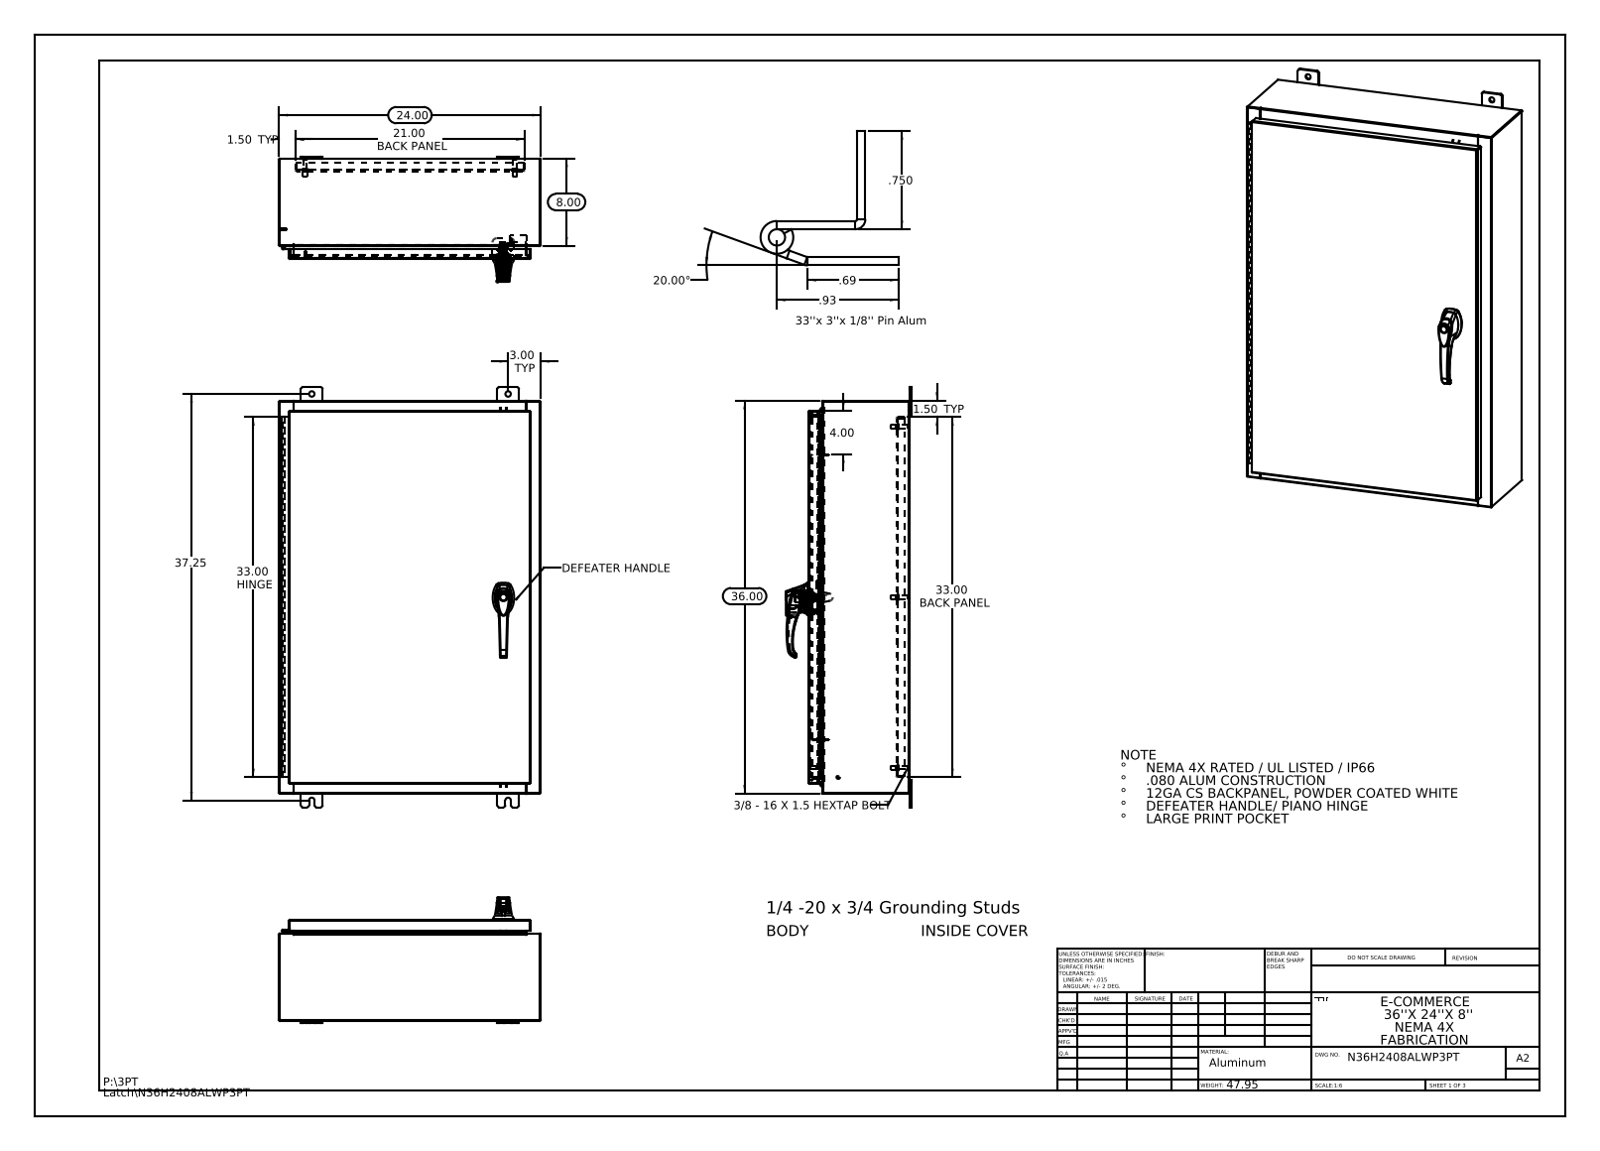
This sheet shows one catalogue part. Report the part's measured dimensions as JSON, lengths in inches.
{"part_name": "10_30 CD Stud; N36H2408ALWP3PT Backpanel; N36H2408ALWP3PT Hinge Cover Side; 297026 (+8 more)", "step_written_by": "SolidWorks 2013 (CONFIG_CONTROL_DESIGN)", "units": "inches", "bodies": {"solids": 39, "faces": 2856, "planar": 1053, "cylindrical": 1085, "other": 718}, "overall_size": [38.5, 24, 11.495], "volume_in3": 318.5, "surface_area_in2": 7860, "round_holes": [[0.5, 10], [0.25, 4], [0.138, 3], [0.161, 3], [0.079, 2], [0.203, 2], [0.313, 2], [0.437, 2], [0.125, 1], [0.125, 1], [0.197, 1], [0.276, 1]], "round_bosses_or_shafts": [[0.625, 6], [0.375, 6], [0.33, 6], [0.157, 4], [0.14, 4], [0.315, 3], [0.236, 3], [1.181, 1]], "partial_cylinders_radius": [[0.118, 37], [0.006, 33], [0.013, 24], [0.19, 24], [0.088, 18], [0.039, 15], [0.028, 12], [0.008, 6]], "face_to_face_distances": [0.075, 9.126, 0.104, 9.051, 9.201, 1, 1.075, 8.051, 8.126, 1.179], "hole_center_spacings": [11.363, 13.669, 15.625, 24.793, 19.25, 0.295, 0.625, 0.841]}
